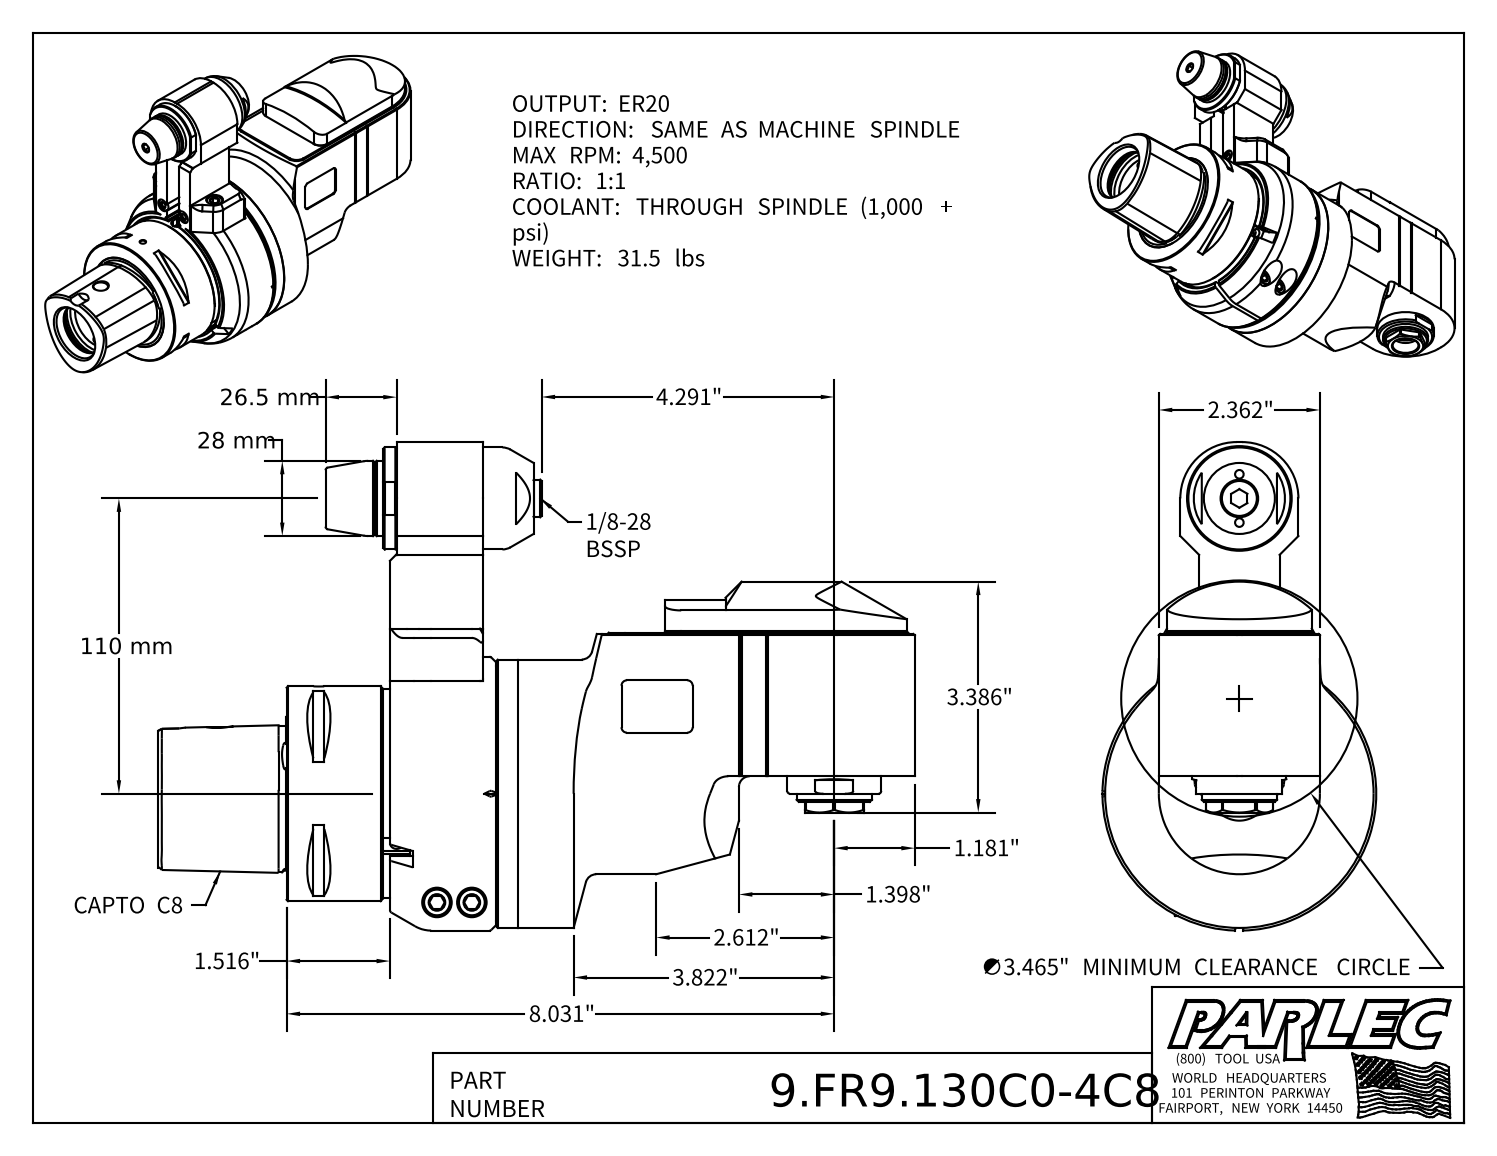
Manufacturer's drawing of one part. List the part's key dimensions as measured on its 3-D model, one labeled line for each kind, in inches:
Part name (STEP PRODUCT): 9.FR9.130C0-4C8
STEP written by: Autodesk Inventor 2022 (AUTOMOTIVE_DESIGN)
Units: inches
Bodies: 3 solids, 574 faces (276 planar, 142 cylindrical, 156 other)
Overall size (bounding box): 11.102 × 7.164 × 4.016
Volume: 88.44 in³ · Surface area: 233 in²
Round holes (diameter × count): ⌀0.126 ×2, ⌀0.13 ×2, ⌀0.157 ×2, ⌀0.165 ×2, ⌀0.197 ×2, ⌀0.256 ×2, ⌀0.315 ×2, ⌀0.409 ×2, ⌀0.433 ×2, ⌀0.709 ×2, ⌀1.142 ×2, ⌀0.098 ×1
Round bosses / shafts (diameter × count): ⌀0.394 ×6, ⌀1.102 ×2, ⌀0.472 ×2, ⌀0.236 ×2, ⌀4.016 ×1, ⌀3.937 ×1, ⌀3.929 ×1, ⌀3.74 ×1
Partial cylindrical surfaces — rounded edges, fillets, slot ends (radius × count): R0.039 ×14, R0.118 ×6, R0.079 ×4, R0.157 ×4, R0.236 ×3, R0.02 ×2, R0.201 ×2, R0.315 ×2
Main face-to-face distances: 0.039, 2.362, 1.811, 0.197, 0.276, 1.122, 1.457, 0.65, 1.772, 0.335
Hole centre spacings: 0.354, 0.709, 2, 2.039, 2.389, 2.739, 7.559, 9.016
